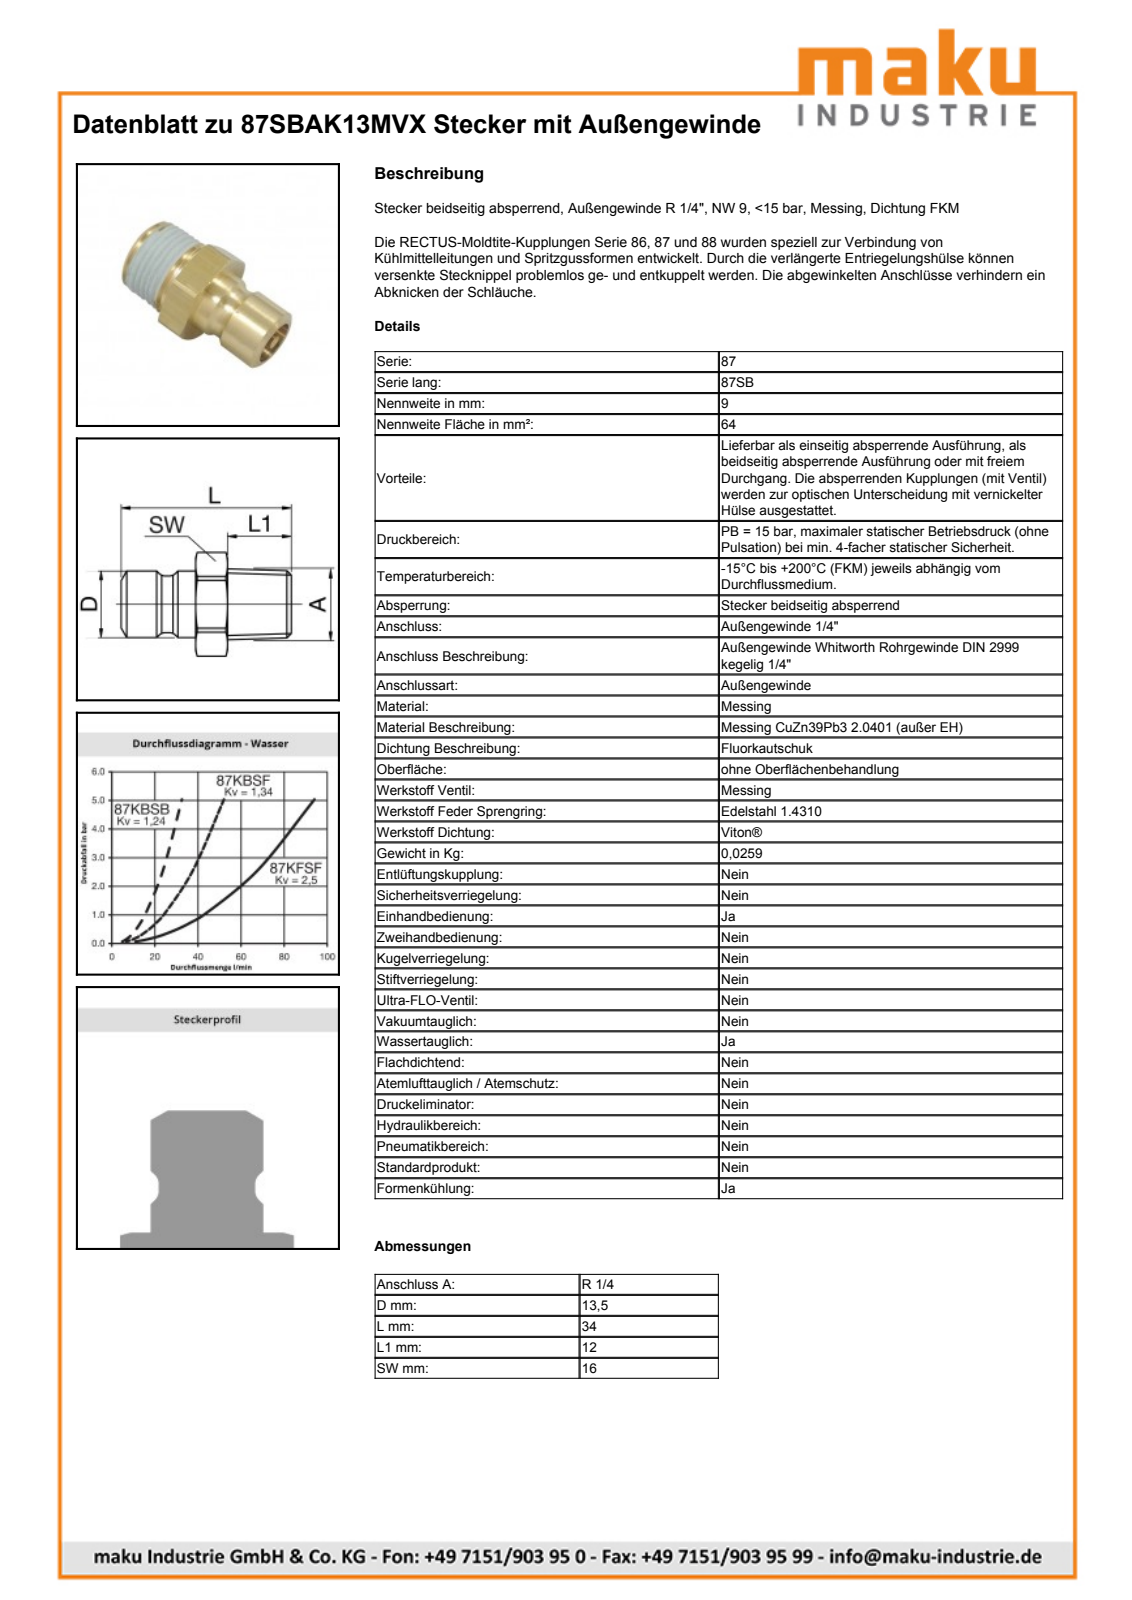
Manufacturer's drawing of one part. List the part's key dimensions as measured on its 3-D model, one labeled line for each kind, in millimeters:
Part name (STEP PRODUCT): D107725
STEP written by: Autodesk Inventor 2013 (AUTOMOTIVE_DESIGN)
Units: millimetres
Bodies: 1 solid, 38 faces (10 planar, 9 cylindrical, 19 other)
Overall size (bounding box): 34 × 18.05 × 16
Volume: 5 155 mm³ · Surface area: 1 902 mm²
Round bosses / shafts (diameter × count): ⌀13.5 ×1, ⌀11.5 ×1
Partial cylindrical surfaces — rounded edges, fillets, slot ends (radius × count): R9.03 ×1
Main face-to-face distances: 16, 34, 15.5, 18.5, 22, 6.5, 12
